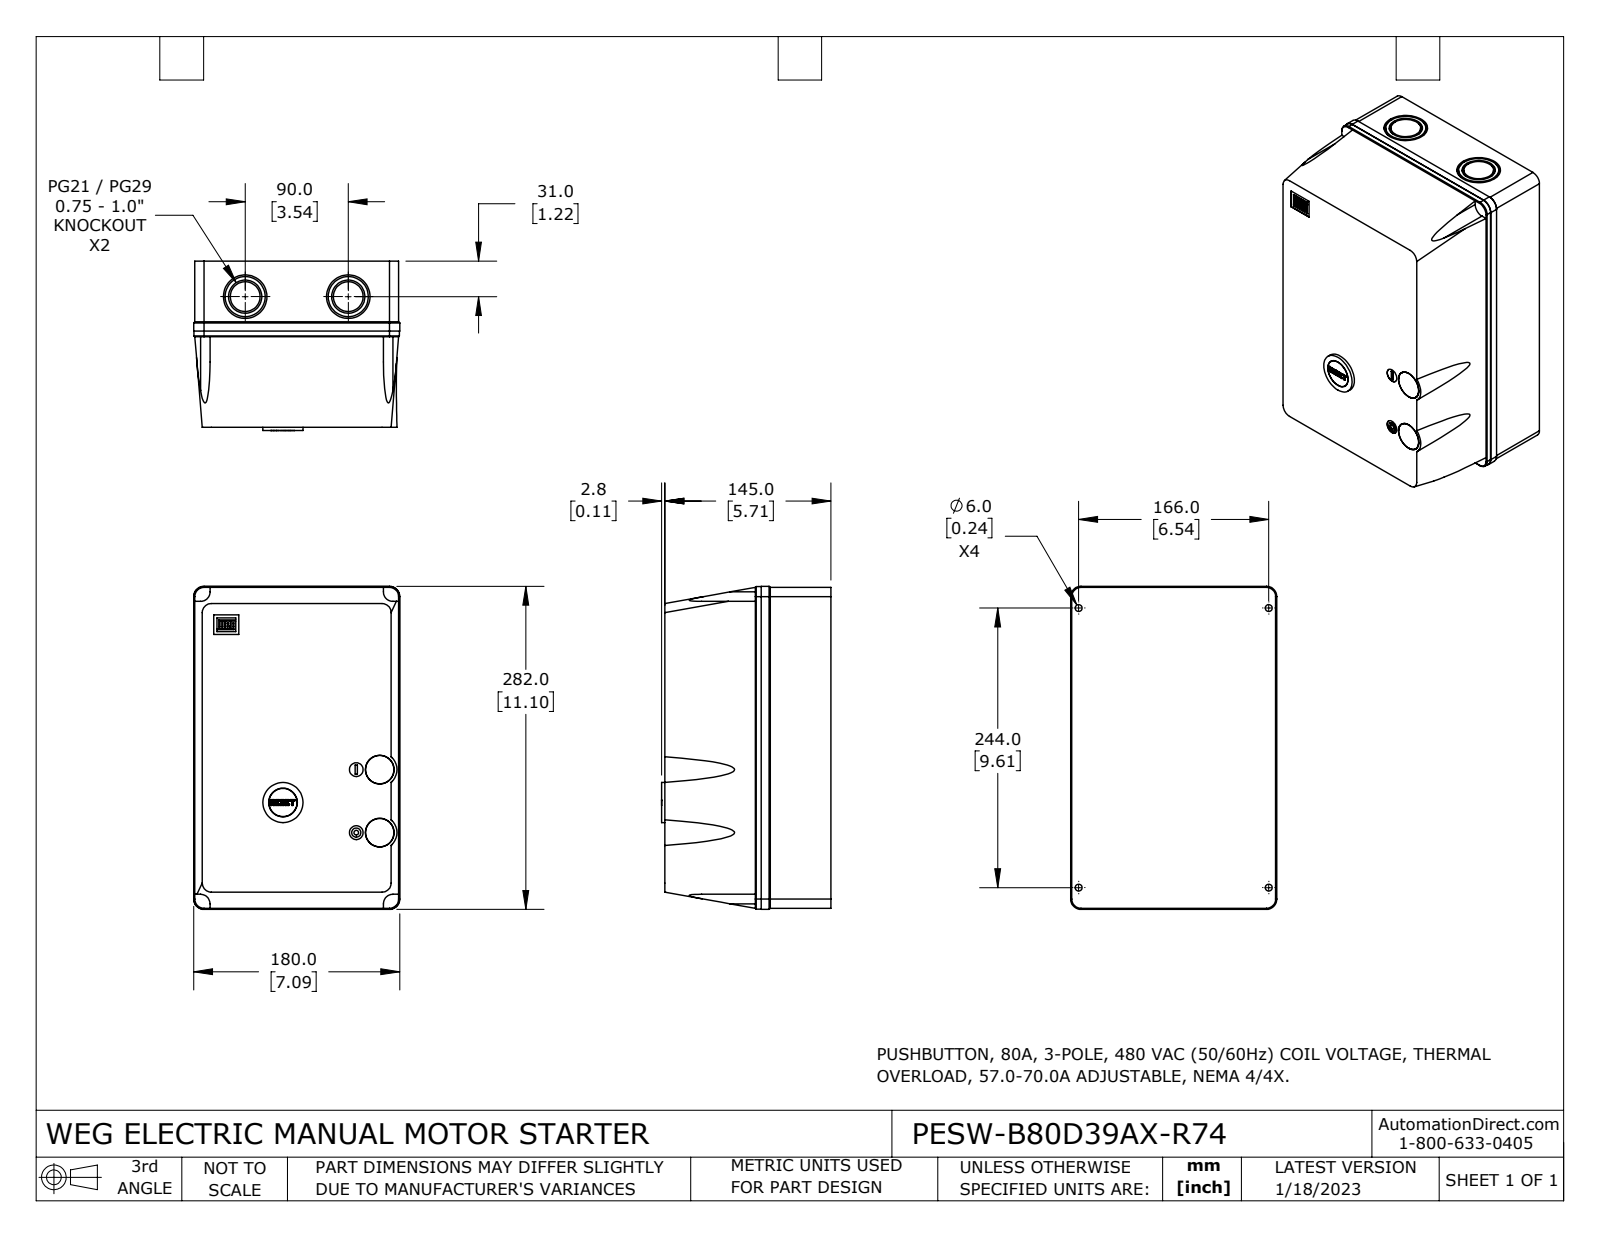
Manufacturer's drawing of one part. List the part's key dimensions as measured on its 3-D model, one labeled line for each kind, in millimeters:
Part name (STEP PRODUCT): PESW-B80D39AX-R74
STEP written by: SolidWorks 2021 (CONFIG_CONTROL_DESIGN)
Units: millimetres
Bodies: 3 solids, 286 faces (130 planar, 144 cylindrical, 12 other)
Overall size (bounding box): 282 × 180 × 147.9
Volume: 7 014 000 mm³ · Surface area: 232 257 mm²
Round holes (diameter × count): ⌀6 ×4, ⌀25 ×3, ⌀12 ×2, ⌀29 ×2, ⌀38 ×2, ⌀4 ×1, ⌀30.5 ×1
Round bosses / shafts (diameter × count): ⌀35 ×3, ⌀26 ×2, ⌀24.8 ×2, ⌀30.3 ×1, ⌀24.6 ×1, ⌀14 ×1, ⌀8 ×1
Partial cylindrical surfaces — rounded edges, fillets, slot ends (radius × count): R0.1 ×34, R8 ×4, R8.3 ×4, R8.7 ×4, R9 ×4, R1.6 ×1
Main face-to-face distances: 145, 178, 280, 1, 0.7, 179, 179.7, 178.7, 281, 180
Hole centre spacings: 20.5, 55, 58.7, 166, 244, 295.11, 49.14, 57.14
